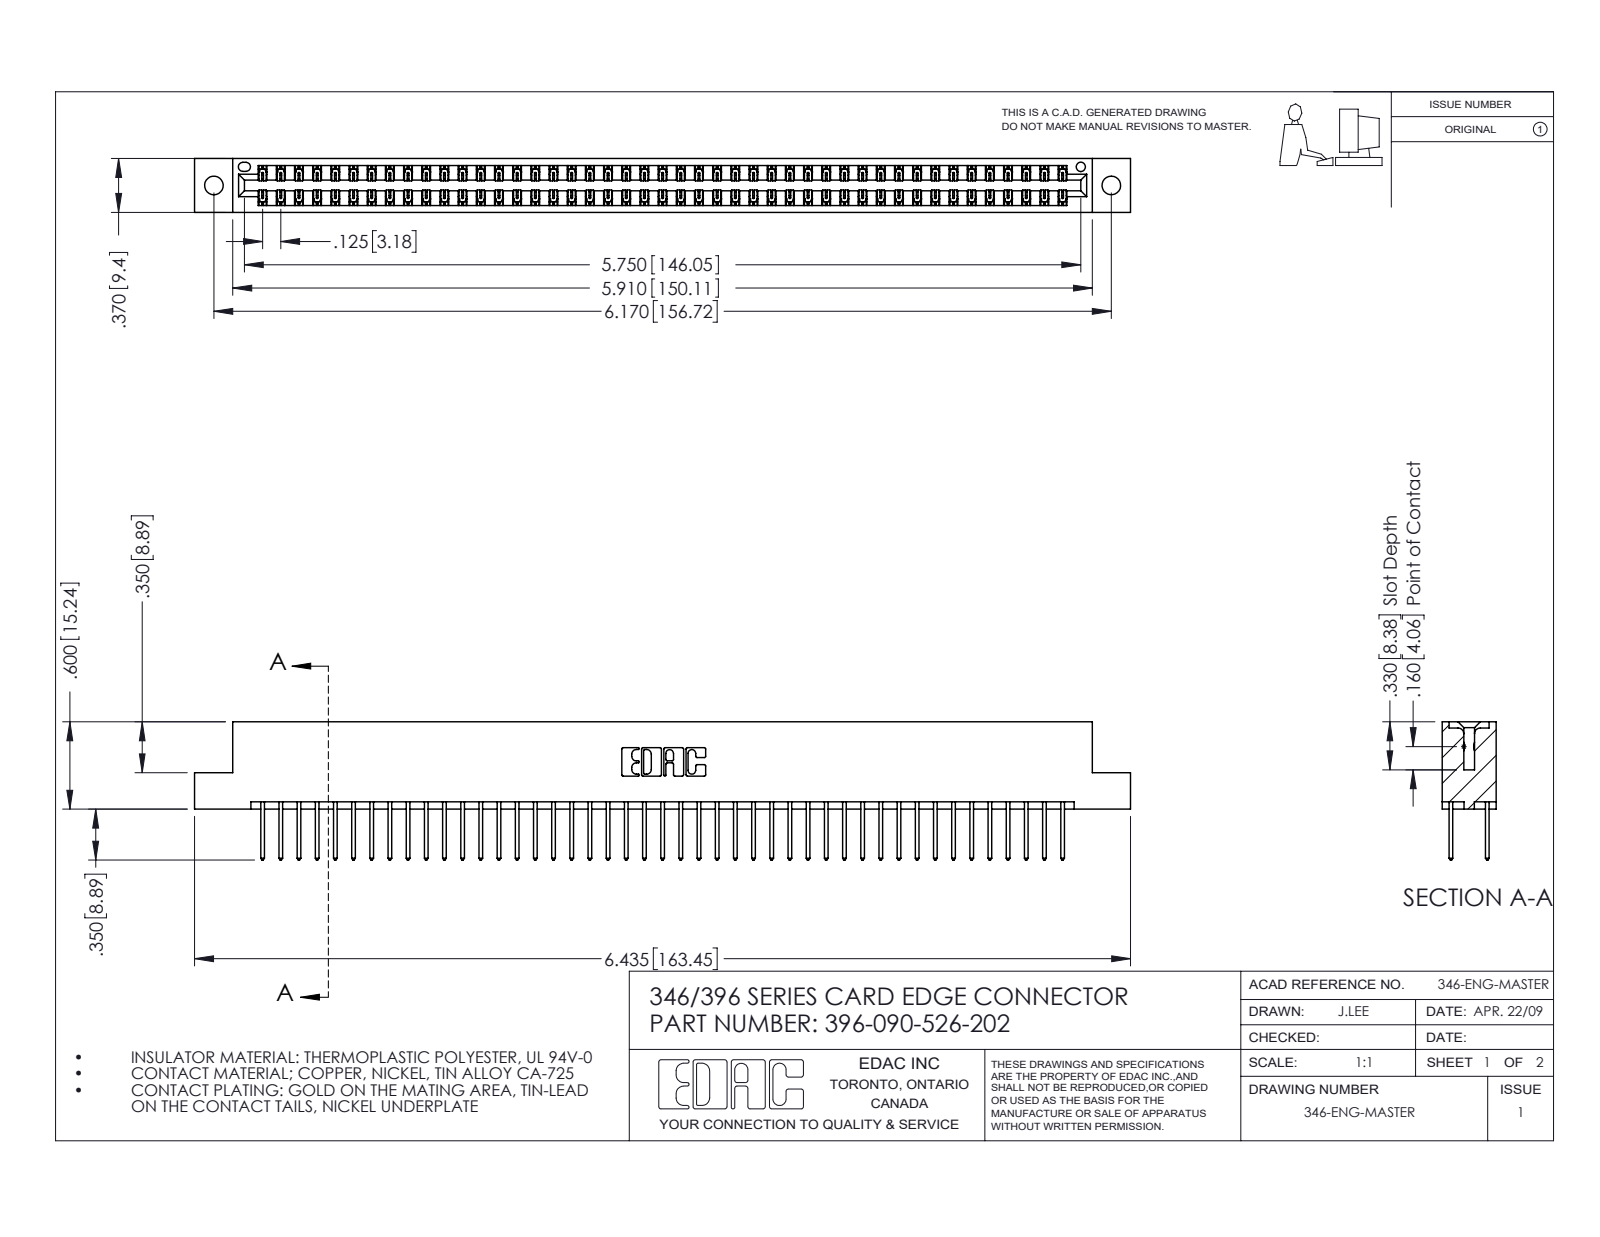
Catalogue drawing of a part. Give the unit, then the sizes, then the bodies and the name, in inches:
Units: inches
Overall size (bounding box): 6.435 × 0.95 × 0.37
Round holes (diameter × count): ⌀0.128 ×2, ⌀0.064 ×1
Partial cylindrical surfaces — rounded edges, fillets, slot ends (radius × count): R0.006 ×135, R0.01 ×90, R0.01 ×22, R0.007 ×6, R0.031 ×6, R0.026 ×3, R0.014 ×2, R0.022 ×2
Main face-to-face distances: 0.048, 0.322, 0.25, 0.37, 0.072, 0.298, 0.025, 0.275, 0.148, 0.222
Hole centre spacings: 0.246, 5.961, 6.17
Volume: 0.981 in³ · Surface area: 34.92 in²
Bodies: 91 solids, 4802 faces (3226 planar, 1576 cylindrical, 0 other)
Part name (STEP PRODUCT): 345-292-001_345-293-126; 396-090-526-202; 346 Part_Flush Mounting Lugs - 0.128 Dia
STEP written by: SolidWorks 2016 (CONFIG_CONTROL_DESIGN)
